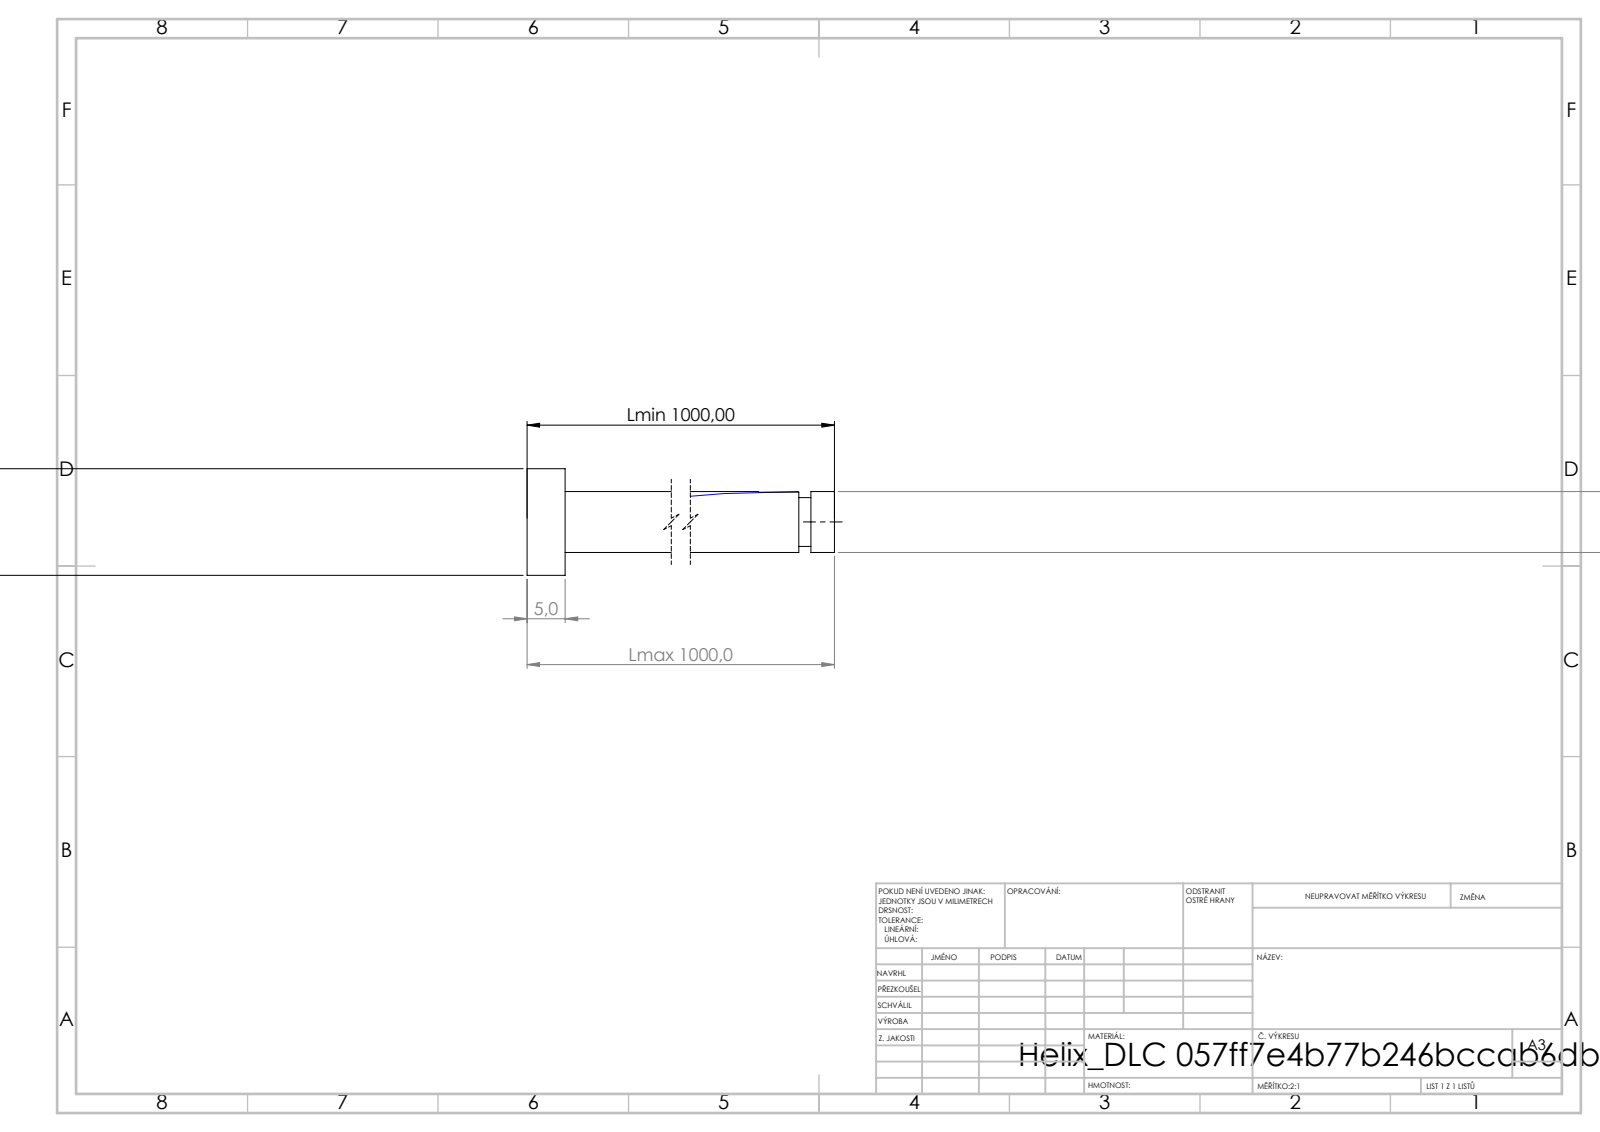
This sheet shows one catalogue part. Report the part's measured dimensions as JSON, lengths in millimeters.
{"step_written_by": "SolidWorks 2019 (CONFIG_CONTROL_DESIGN)", "units": "millimeters", "bodies": {"solids": 1, "faces": 16, "planar": 6, "cylindrical": 9, "other": 1}, "overall_size": [1000, 14, 14], "volume_mm3": 61444, "surface_area_mm2": 34322, "round_bosses_or_shafts": [[14, 1], [8, 1], [6.4, 1]], "face_to_face_distances": [5, 1000, 995, 996.92, 991.92, 3.08, 995.32, 990.32, 1.6, 4.68]}
